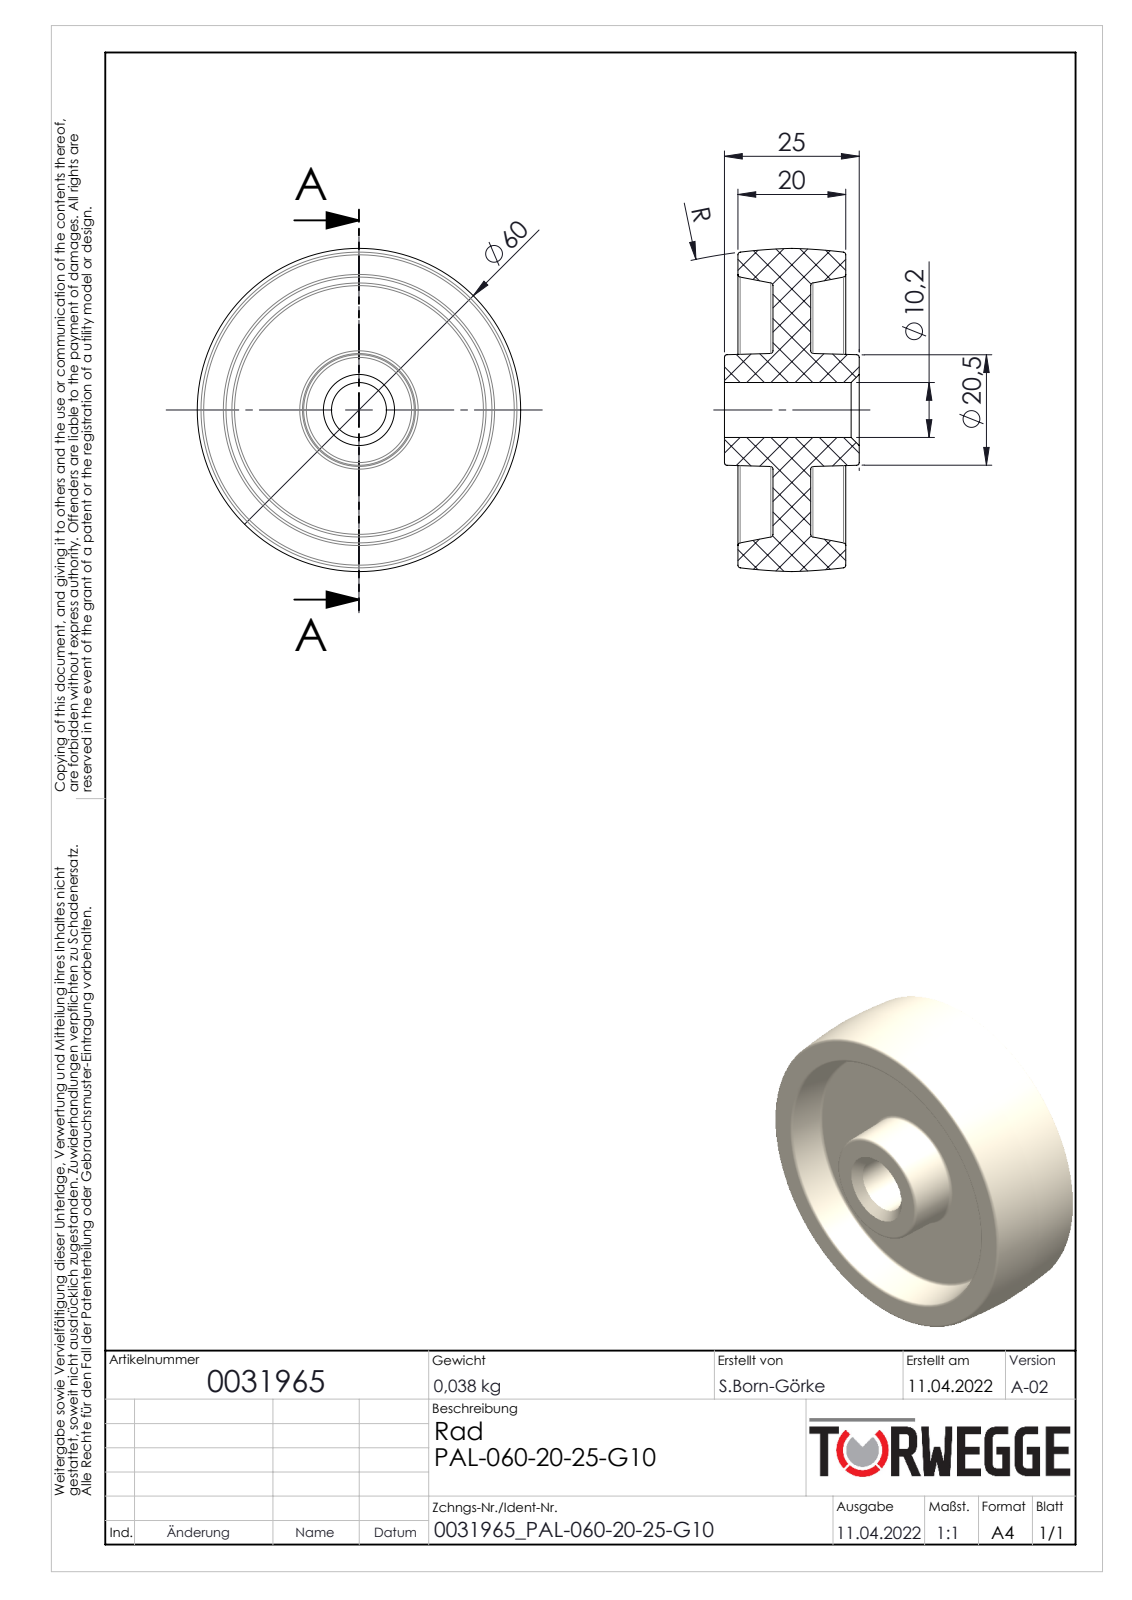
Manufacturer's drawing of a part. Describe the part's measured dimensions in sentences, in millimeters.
The part is named "0031965". Its 3-D file was written by "SolidWorks 2020 (AUTOMOTIVE_DESIGN)". It is 1 solid with 42 faces: 6 planar, 2 cylindrical and 34 other. Overall it measures 60 by 60 by 25 millimeters. Its volume is 35 675 cubic millimeters and its surface area 12 309 square millimeters. Round holes: 1 of diameter 10.2. The main face-to-face distances are 7, 6.5, 13.5, 20, 2.5, 9, 16, 22.5, 25.
